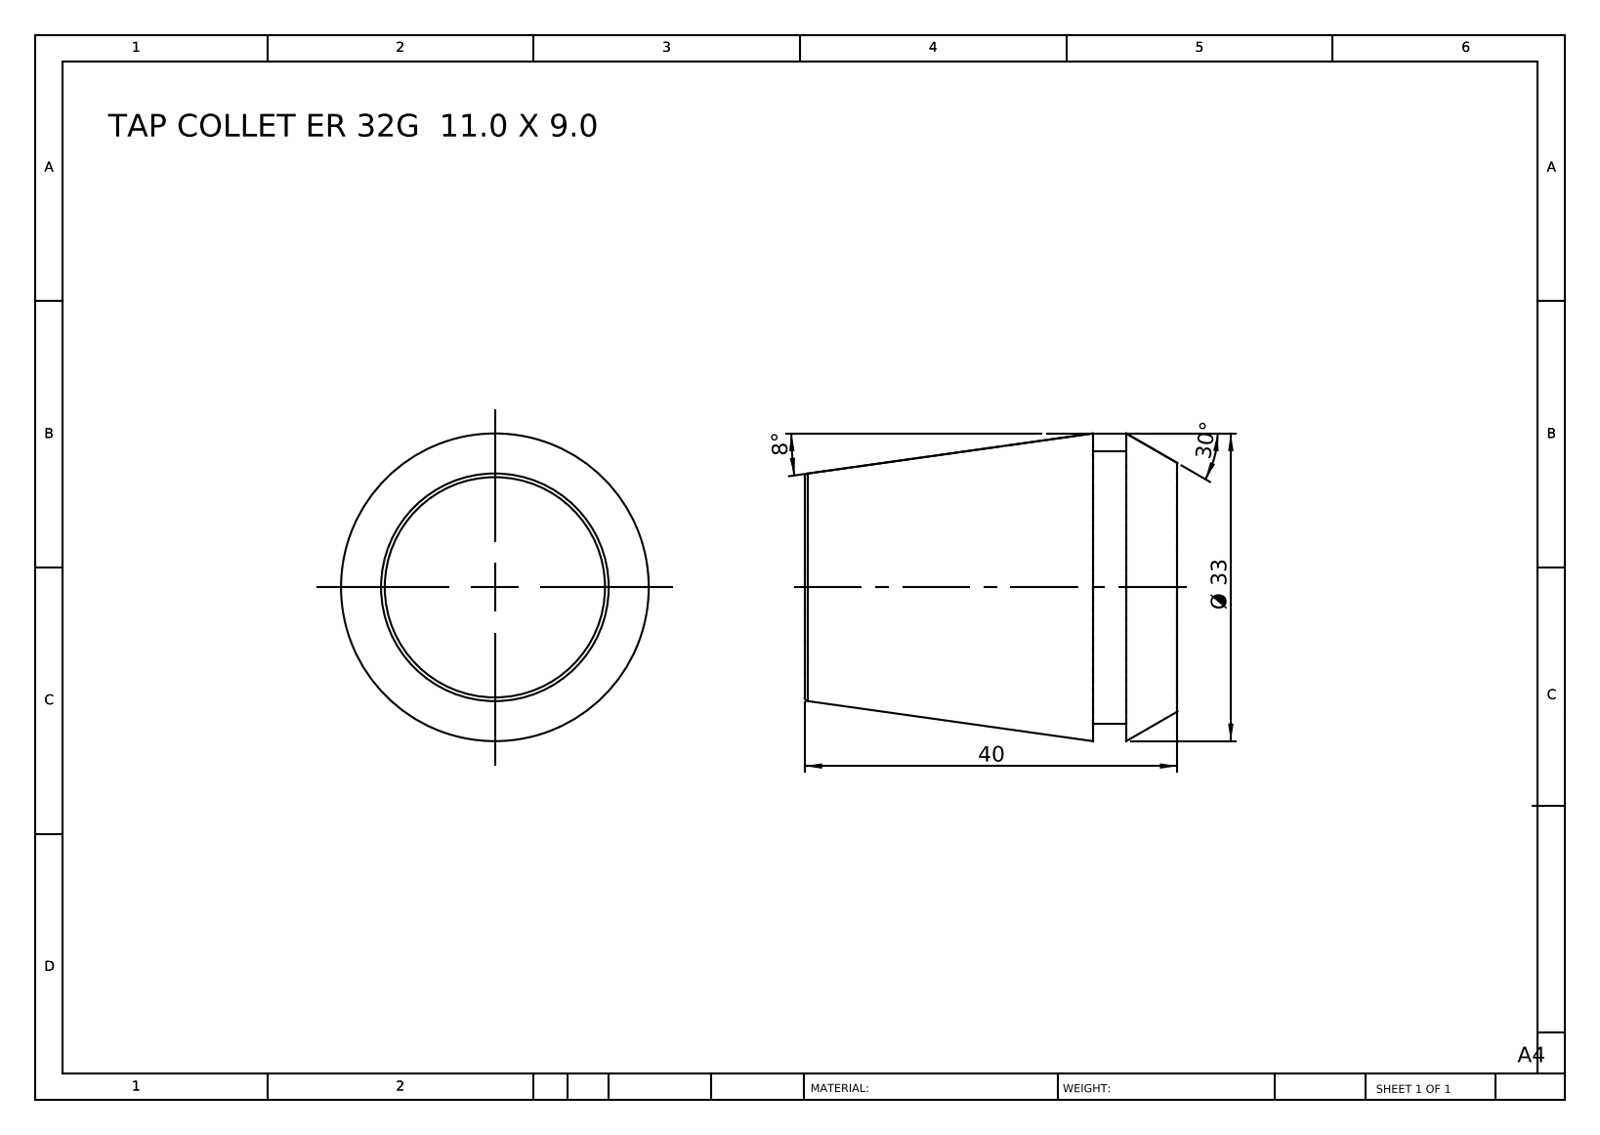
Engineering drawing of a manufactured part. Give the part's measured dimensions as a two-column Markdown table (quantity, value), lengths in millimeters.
| quantity | value |
| --- | --- |
| part name | TAP COLLET ER 32G 11.0 X 9.0 |
| STEP written by | SolidWorks 2014 (CONFIG_CONTROL_DESIGN) |
| units | millimeters |
| bodies | 1 solid, 12 faces (4 planar, 2 cylindrical, 6 other) |
| overall size | 40 × 33 × 33 |
| volume | 26 350 mm³ |
| surface area | 5 119 mm² |
| round bosses / shafts (diameter × count) | 29.2 × 1 |
| main face-to-face distances | 40, 9.1, 30.9, 5.5, 3.6, 34.5 |
